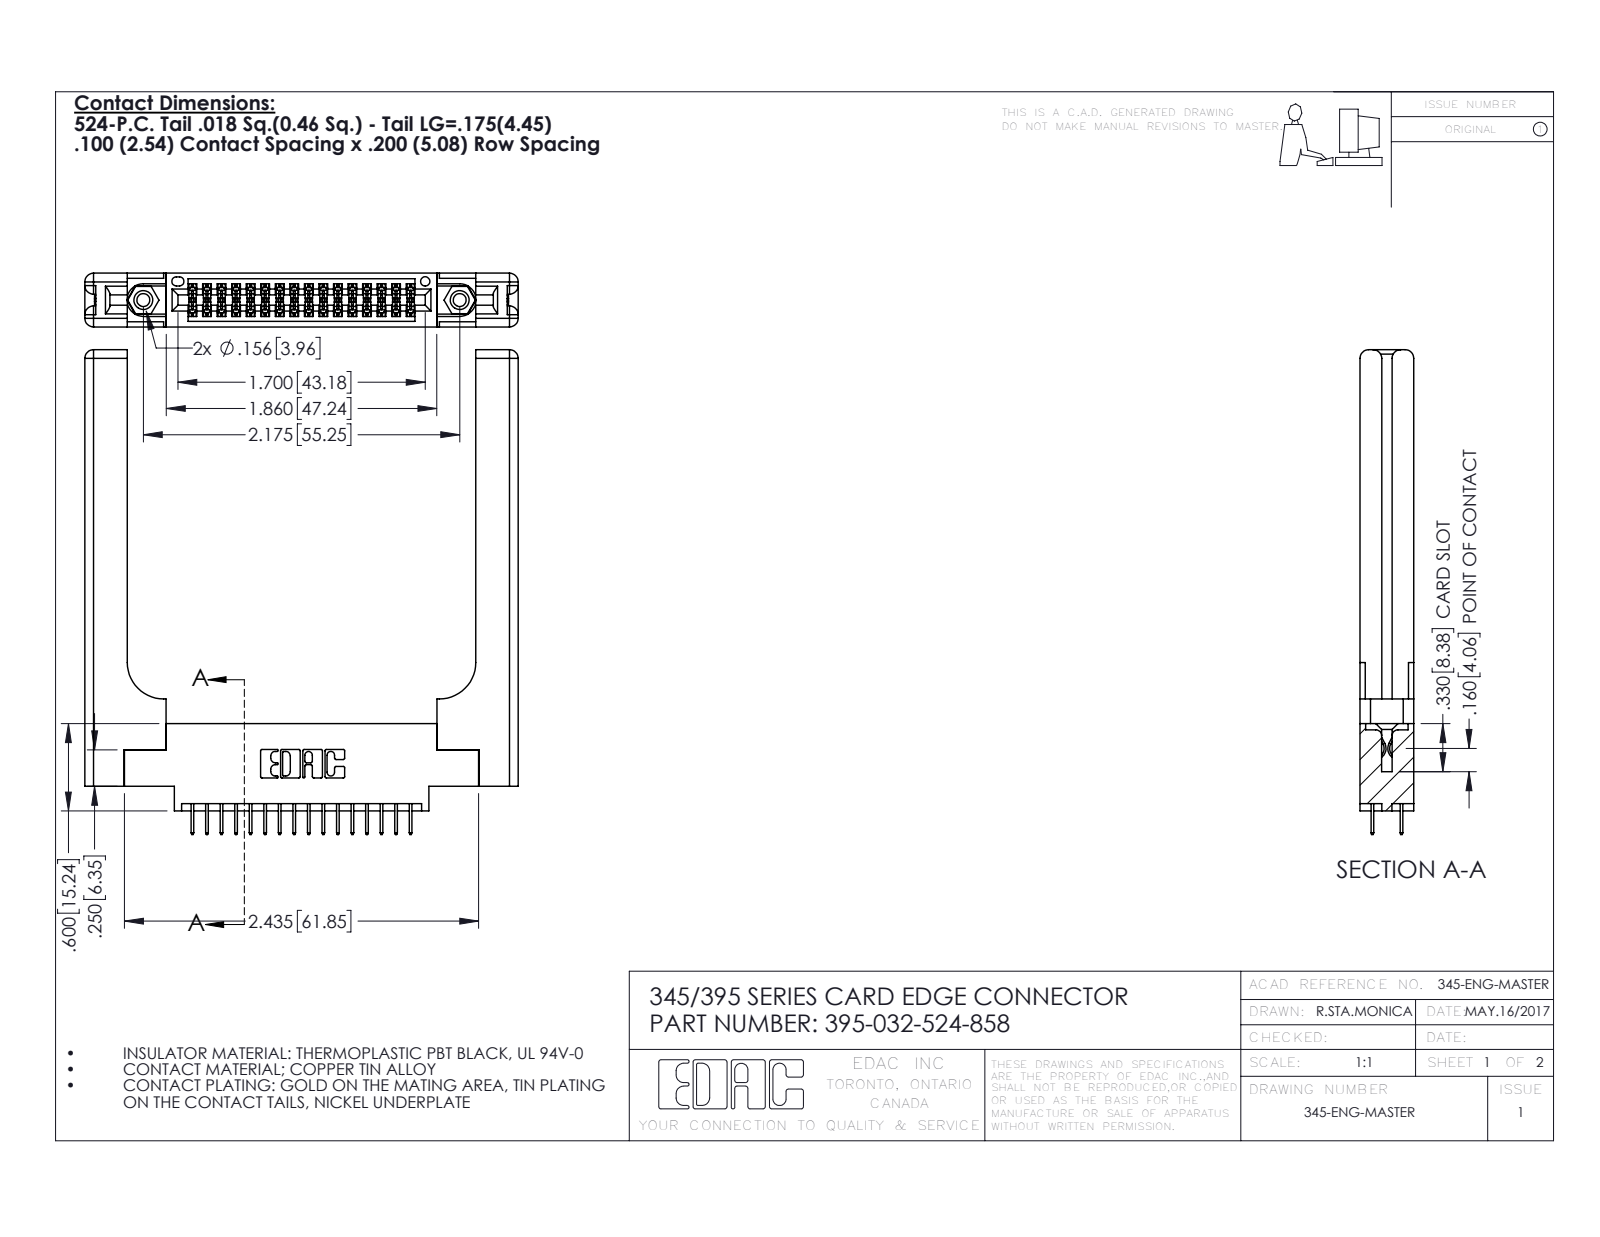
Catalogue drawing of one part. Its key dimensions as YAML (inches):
part_name: "345 Part_0.170 Offset - 0.156 Dia-TH; 345-250-001_345-250-001-102; 345-220-058_345-220-058; 395-032-524-858 (+1 more)"
step_written_by: "SolidWorks 2016 (CONFIG_CONTROL_DESIGN)"
units: inches
bodies: {solids: 37, faces: 2114, planar: 1480, cylindrical: 574, other: 60}
overall_size: [3.332, 2.979, 0.37]
volume: 0.941
surface_area: 23
round_holes:
  - {diameter: 0.089, count: 2}
  - {diameter: 0.125, count: 2}
  - {diameter: 0.156, count: 2}
  - {diameter: 0.064, count: 1}
round_bosses_or_shafts:
  - {diameter: 0.155, count: 2}
partial_cylinders:
  - {radius: 0.006, count: 48}
  - {radius: 0.01, count: 22}
  - {radius: 0.06, count: 16}
  - {radius: 0.007, count: 6}
  - {radius: 0.031, count: 6}
  - {radius: 0.026, count: 3}
  - {radius: 0.014, count: 2}
  - {radius: 0.019, count: 2}
face_to_face_distances: [0.37, 0.072, 0.298, 0.15, 0.148, 0.077, 0.22, 0.225, 0.123, 0.098]
hole_center_spacings: [0.27, 1.942, 2.175]
